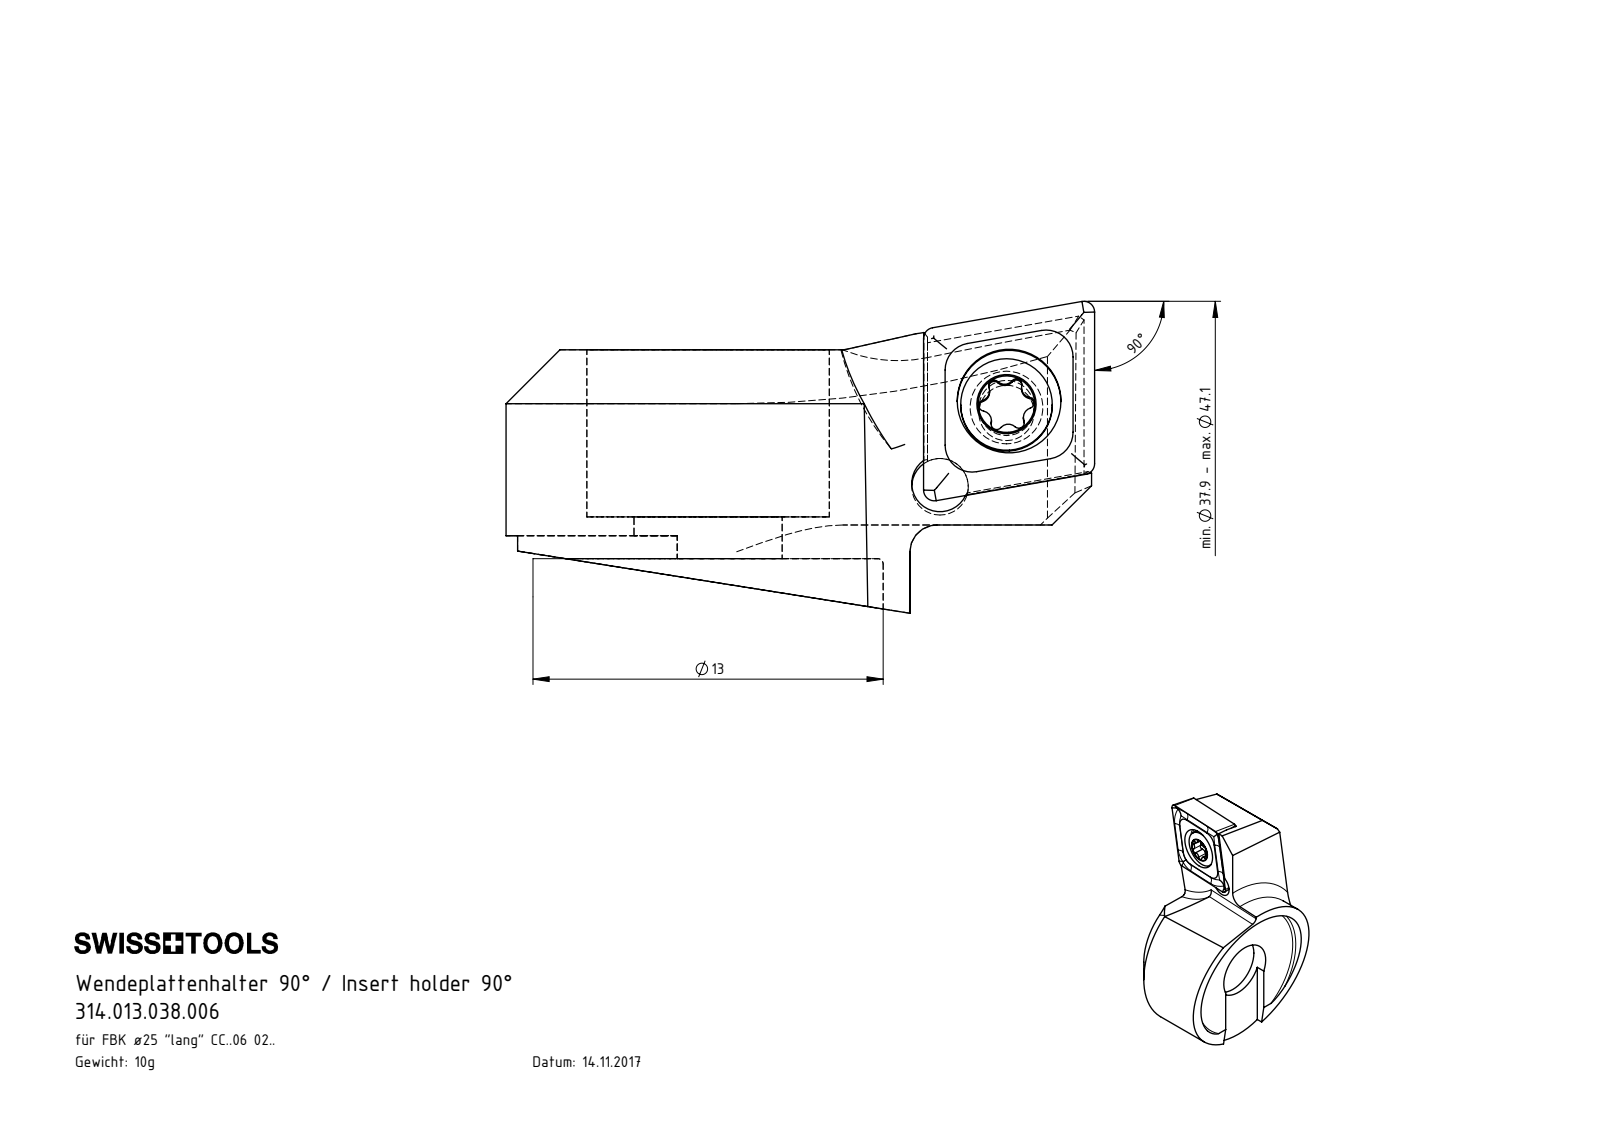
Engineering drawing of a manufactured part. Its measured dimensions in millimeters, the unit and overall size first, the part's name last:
Units: millimetres
Overall size (bounding box): 21.85 × 15 × 11.58
Round holes (diameter × count): ⌀2.05 ×1, ⌀2.1 ×1, ⌀2.8 ×1, ⌀3.85 ×1, ⌀5.5 ×1, ⌀9 ×1
Round bosses / shafts (diameter × count): ⌀15 ×1, ⌀3.4 ×1, ⌀2.5 ×1
Partial cylindrical surfaces — rounded edges, fillets, slot ends (radius × count): R0.21 ×6, R0.36 ×5, R0.5 ×2, R0.36 ×1, R1.05 ×1, R6.4 ×1, R6.5 ×1, R9 ×1
Main face-to-face distances: 7.75, 7.65, 2.28, 6.2, 6.1, 1.55, 6.5, 6.4, 1.25, 6.9
Hole centre spacings: 3.84, 3.99
Volume: 1 269 mm³ · Surface area: 1 570 mm²
Bodies: 5 solids, 148 faces (48 planar, 45 cylindrical, 55 other)
Part name (STEP PRODUCT): Kopie von F25-WCA.001.009_C^F25-WCA.001.009_fertigbearbeitet; CCMT060204; WCA-ER2.001.006_A; 314.013.038.006
STEP written by: SolidWorks 2017 (CONFIG_CONTROL_DESIGN)
